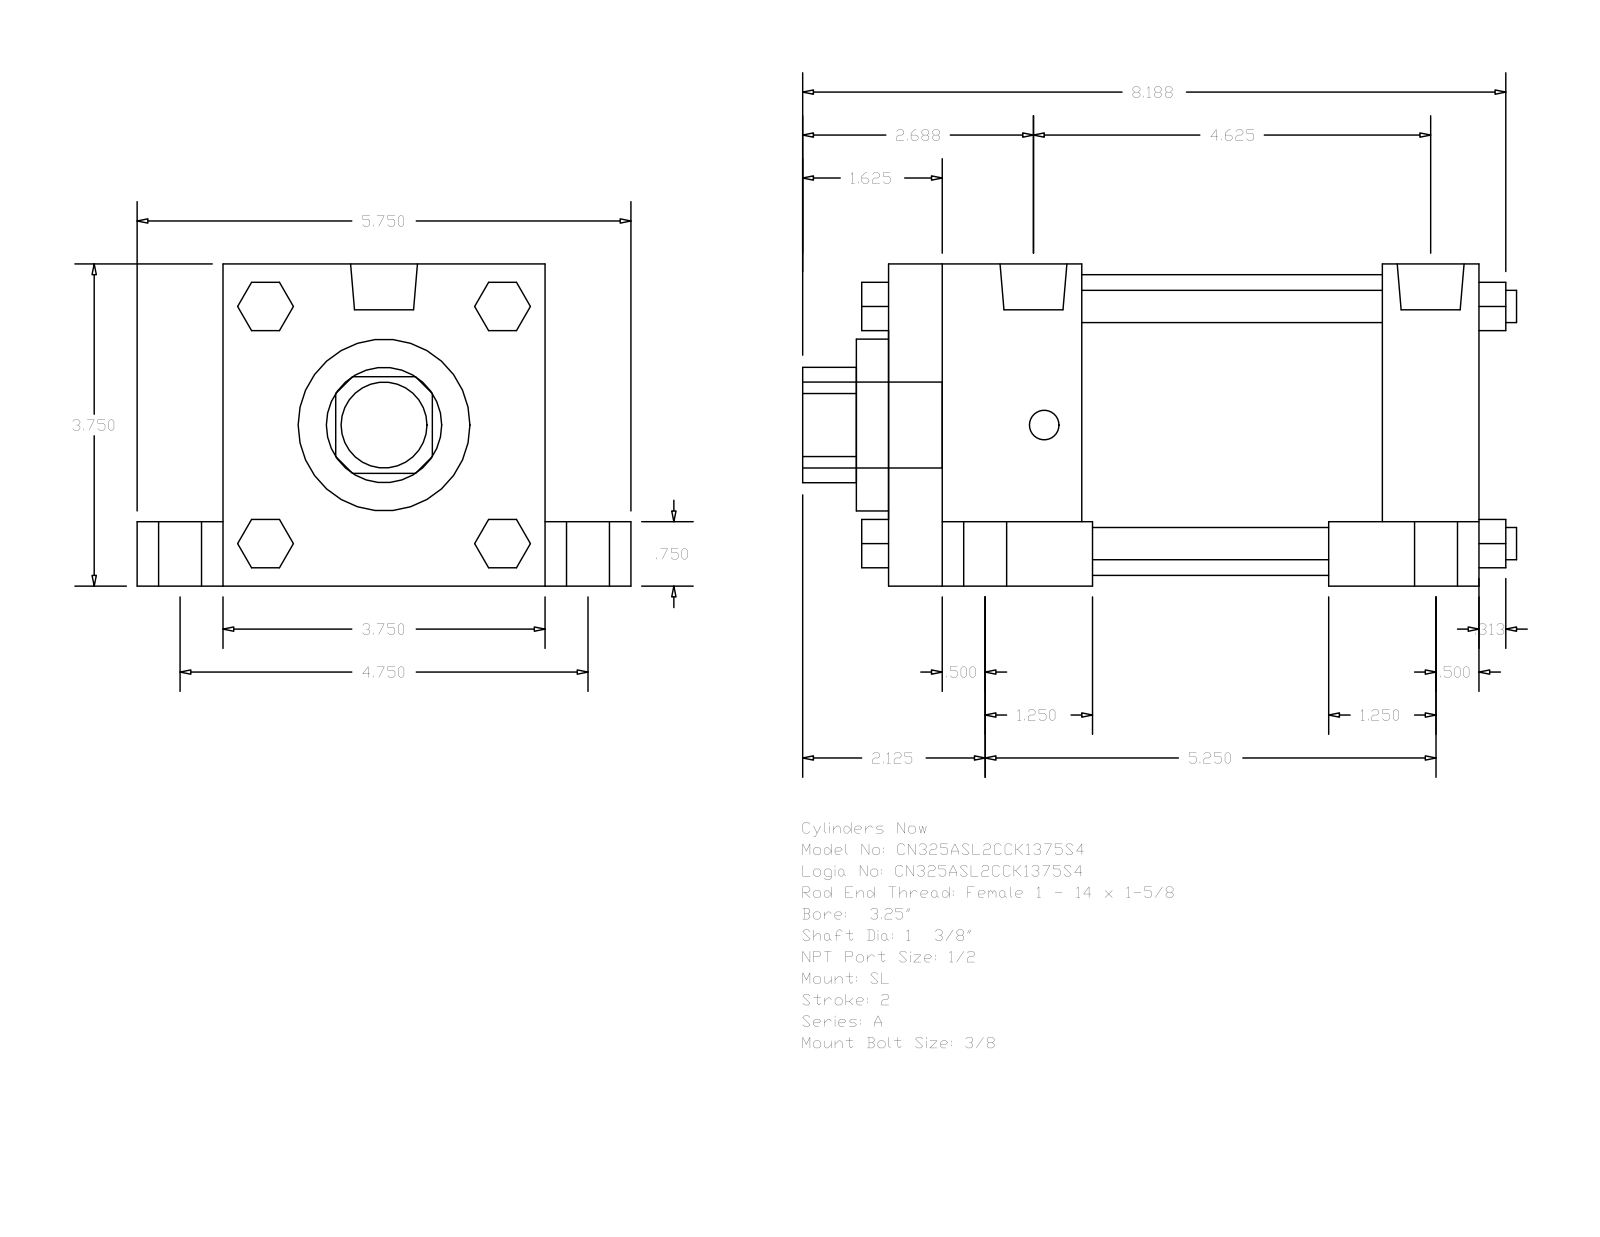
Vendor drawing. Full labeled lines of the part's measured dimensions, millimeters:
Part name (STEP PRODUCT): A_SL__0325_1.375
STEP written by: GSSL Pune (CONFIG_CONTROL_DESIGN)
Units: millimetres
Bodies: 0 solids, 150 faces (114 planar, 36 cylindrical, 0 other)
Overall size (bounding box): 211.14 × 146.05 × 95.25
Round holes (diameter × count): ⌀34.92 ×1, ⌀50.8 ×1, ⌀88.9 ×1
Round bosses / shafts (diameter × count): ⌀19.05 ×4, ⌀12.7 ×4, ⌀9.53 ×4, ⌀8.73 ×4, ⌀19.77 ×2, ⌀25.4 ×1
Partial cylindrical surfaces — rounded edges, fillets, slot ends (radius × count): R17.06 ×1
Main face-to-face distances: 95.24, 174.63, 25.41, 120.65, 19.05, 76.19, 28.58, 57.15, 146.05, 88.9
